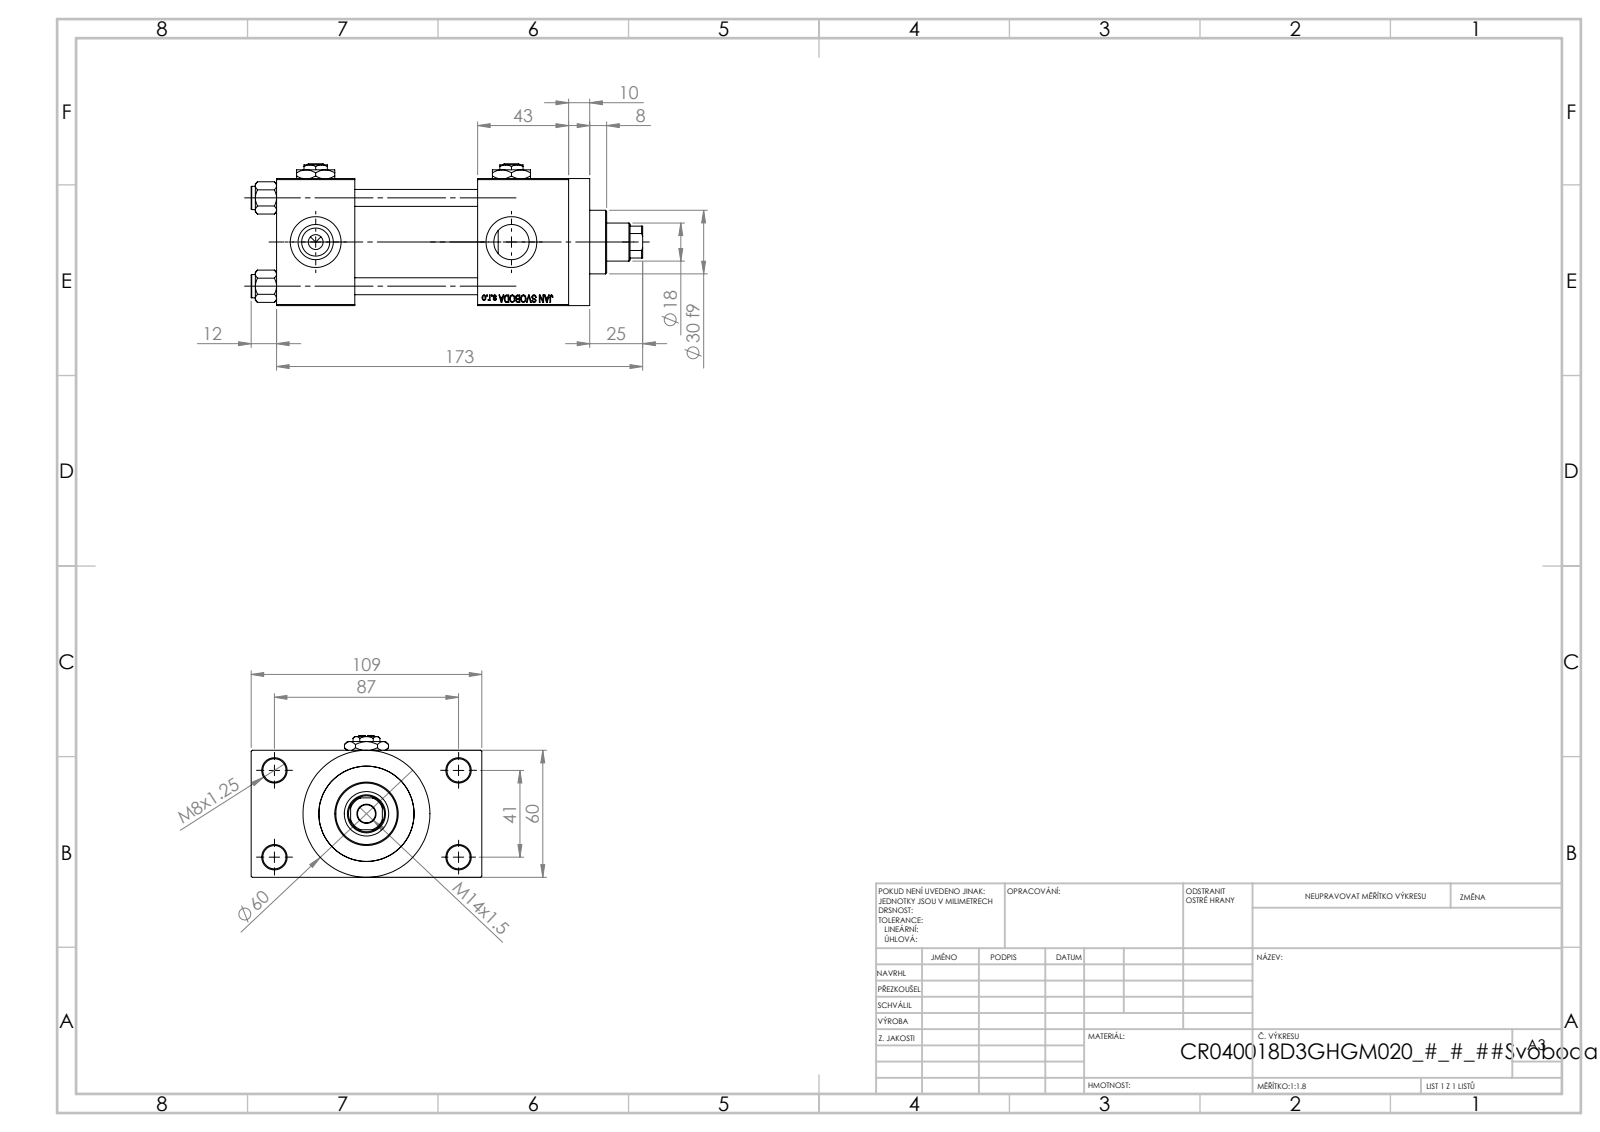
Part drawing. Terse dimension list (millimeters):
name: V215CR_VCP_D; V215_VC_A; V215CR_D_Body; NUT_M5_D (+2 more)
written by: SolidWorks 2019 (CONFIG_CONTROL_DESIGN)
unit: mm
bodies: 13 solids, 1205 faces (546 planar, 99 cylindrical, 560 other)
size: 185 × 109 × 67
volume: 510 337 mm³; area: 125 192 mm²
holes: 4× ⌀8, 4× ⌀11, 4× ⌀16.66, 4× ⌀24, 3× ⌀7, 1× ⌀8.5, 1× ⌀18, 1× ⌀21, 1× ⌀31, 1× ⌀40, 1× ⌀45
bosses: 4× ⌀11, 1× ⌀60, 1× ⌀46, 1× ⌀30
rounds: 1× R8.5
face distances: 60, 58, 24.5, 84.5, 37, 95, 43, 138, 101, 10
hole spacings: 22.65, 29.49, 41.7, 47.15, 48.09, 64.35, 76.49, 41
